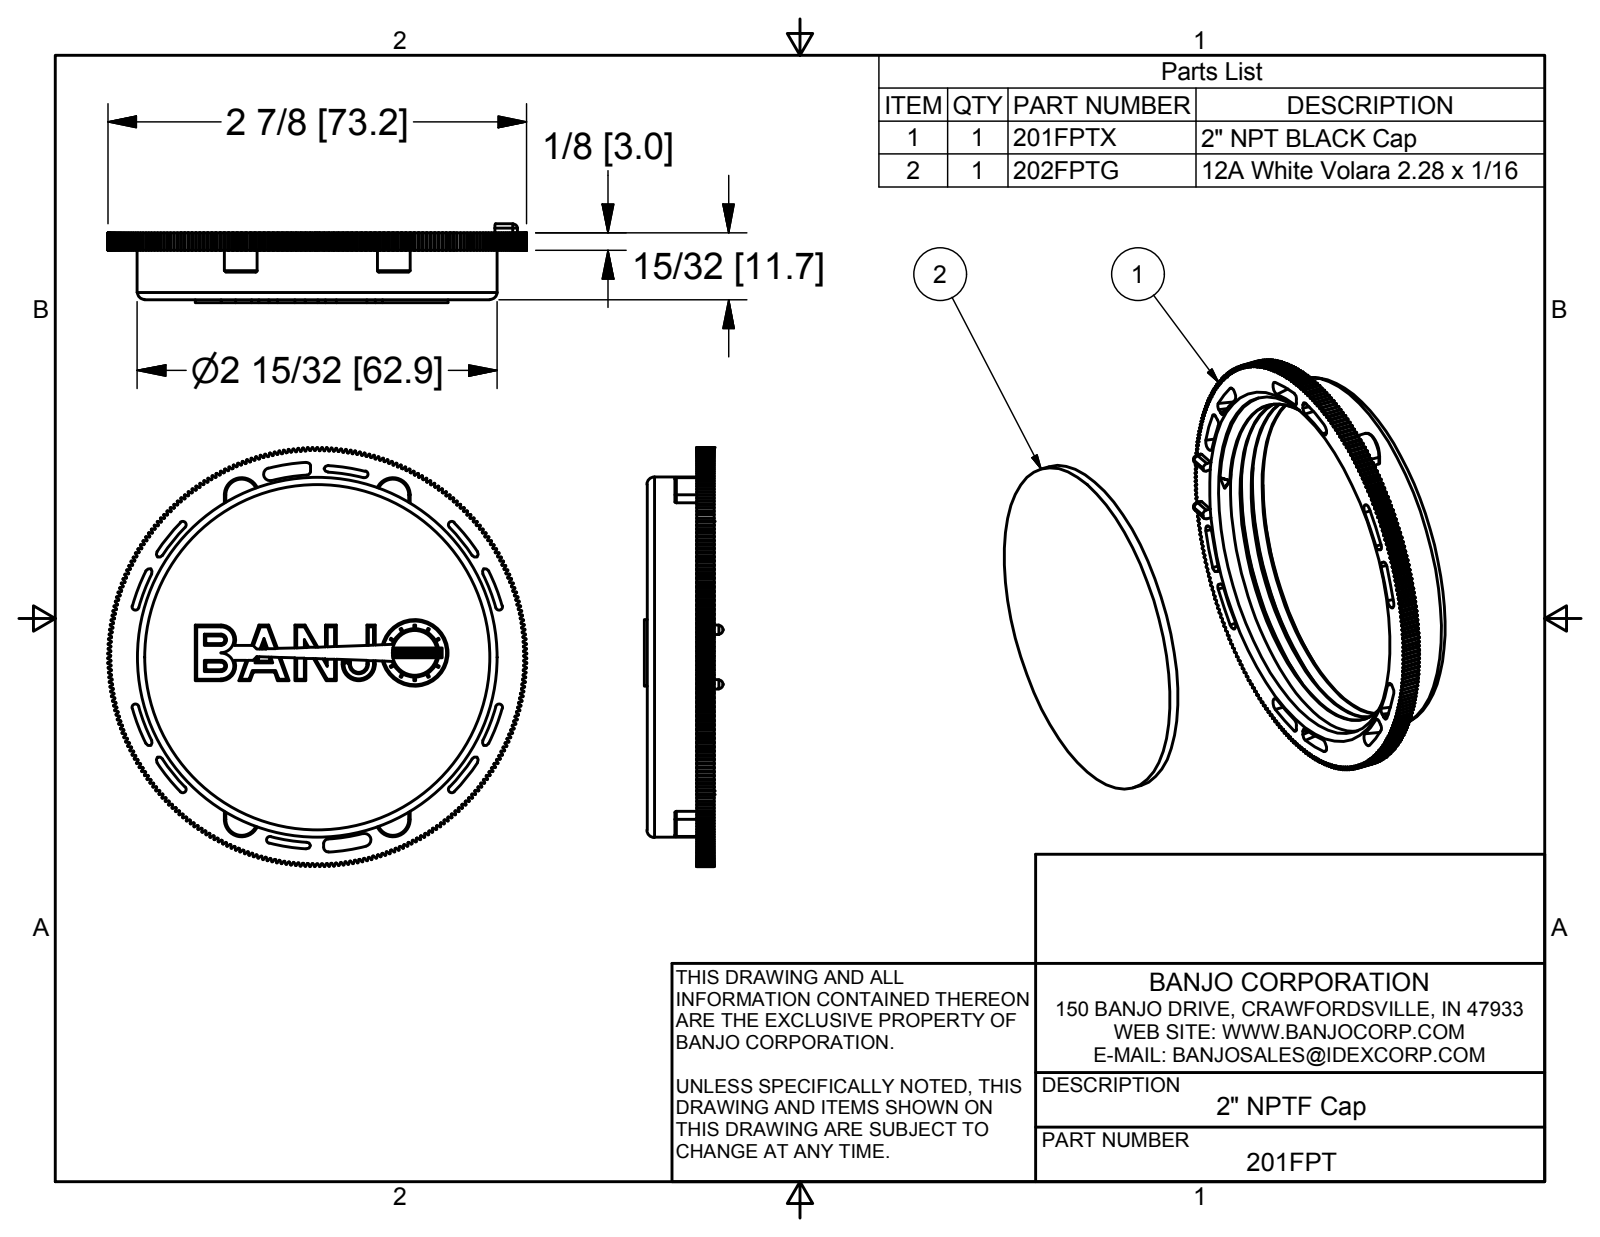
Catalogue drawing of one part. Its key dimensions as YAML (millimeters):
part_name: "201FPTX; 202FPTG; 201FPT"
step_written_by: "Autodesk Inventor 2014 (AUTOMOTIVE_DESIGN)"
units: millimeters
bodies: {solids: 2, faces: 1465, planar: 780, cylindrical: 613, other: 72}
overall_size: [73.15, 73.15, 13.77]
volume: 16816
surface_area: 19957
round_holes:
  - {diameter: 7.84, count: 1}
  - {diameter: 11.08, count: 1}
  - {diameter: 60.71, count: 1}
round_bosses_or_shafts:
  - {diameter: 62.87, count: 1}
  - {diameter: 57.91, count: 1}
  - {diameter: 11.66, count: 1}
partial_cylinders:
  - {radius: 0.76, count: 4}
  - {radius: 3, count: 4}
  - {radius: 0.25, count: 2}
  - {radius: 0.68, count: 2}
  - {radius: 0.81, count: 2}
  - {radius: 0.97, count: 2}
  - {radius: 1.12, count: 2}
  - {radius: 2.28, count: 2}
face_to_face_distances: [2.16, 1.6, 3.76, 4.88, 6.48, 8.64, 9.53, 3.05, 7.93, 11.69]
hole_center_spacings: [17.05]
